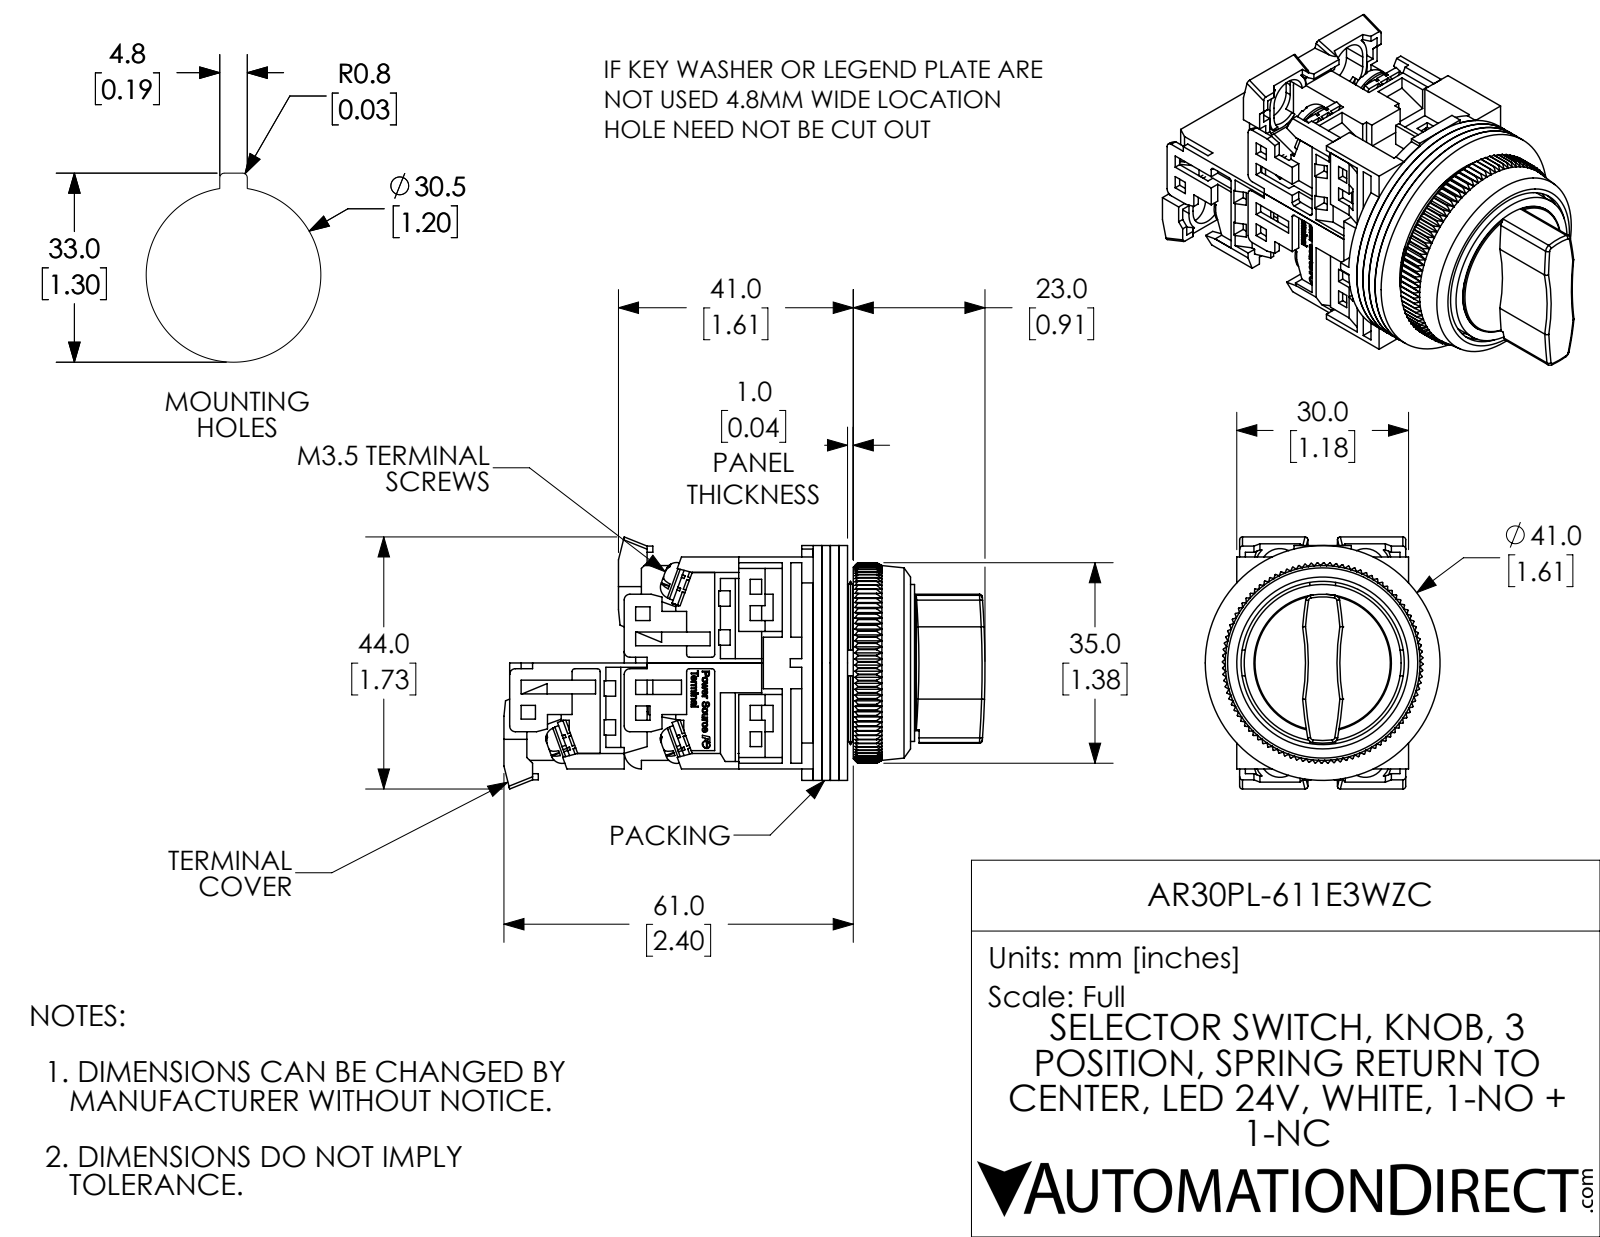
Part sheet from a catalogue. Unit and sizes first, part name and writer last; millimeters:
Units: millimetres
Overall size (bounding box): 84 × 44 × 41
Round holes (diameter × count): ⌀3.5 ×10, ⌀3.6 ×6, ⌀3 ×1, ⌀12 ×1, ⌀18 ×1, ⌀19.5 ×1, ⌀21 ×1, ⌀28.5 ×1, ⌀30 ×1, ⌀31.8 ×1
Round bosses / shafts (diameter × count): ⌀6.6 ×6, ⌀3.5 ×6, ⌀1.6 ×2, ⌀41 ×1, ⌀29.2 ×1, ⌀27.4 ×1, ⌀24 ×1, ⌀22.5 ×1
Partial cylindrical surfaces — rounded edges, fillets, slot ends (radius × count): R1.5 ×24, R0.5 ×14, R1 ×10, R3.5 ×4, R4.5 ×4, R3 ×3, R40 ×2, R75 ×2
Main face-to-face distances: 1.5, 3, 4.5, 1, 20, 1.6, 2, 0.5, 20.6, 17.5
Hole centre spacings: 14.7, 6.8, 16.2, 15.5
Volume: 43 870 mm³ · Surface area: 42 930 mm²
Bodies: 32 solids, 2783 faces (2039 planar, 338 cylindrical, 406 other)
Part name (STEP PRODUCT): AR30PL-611E3WZC
STEP written by: SolidWorks 2017 (AUTOMOTIVE_DESIGN)
